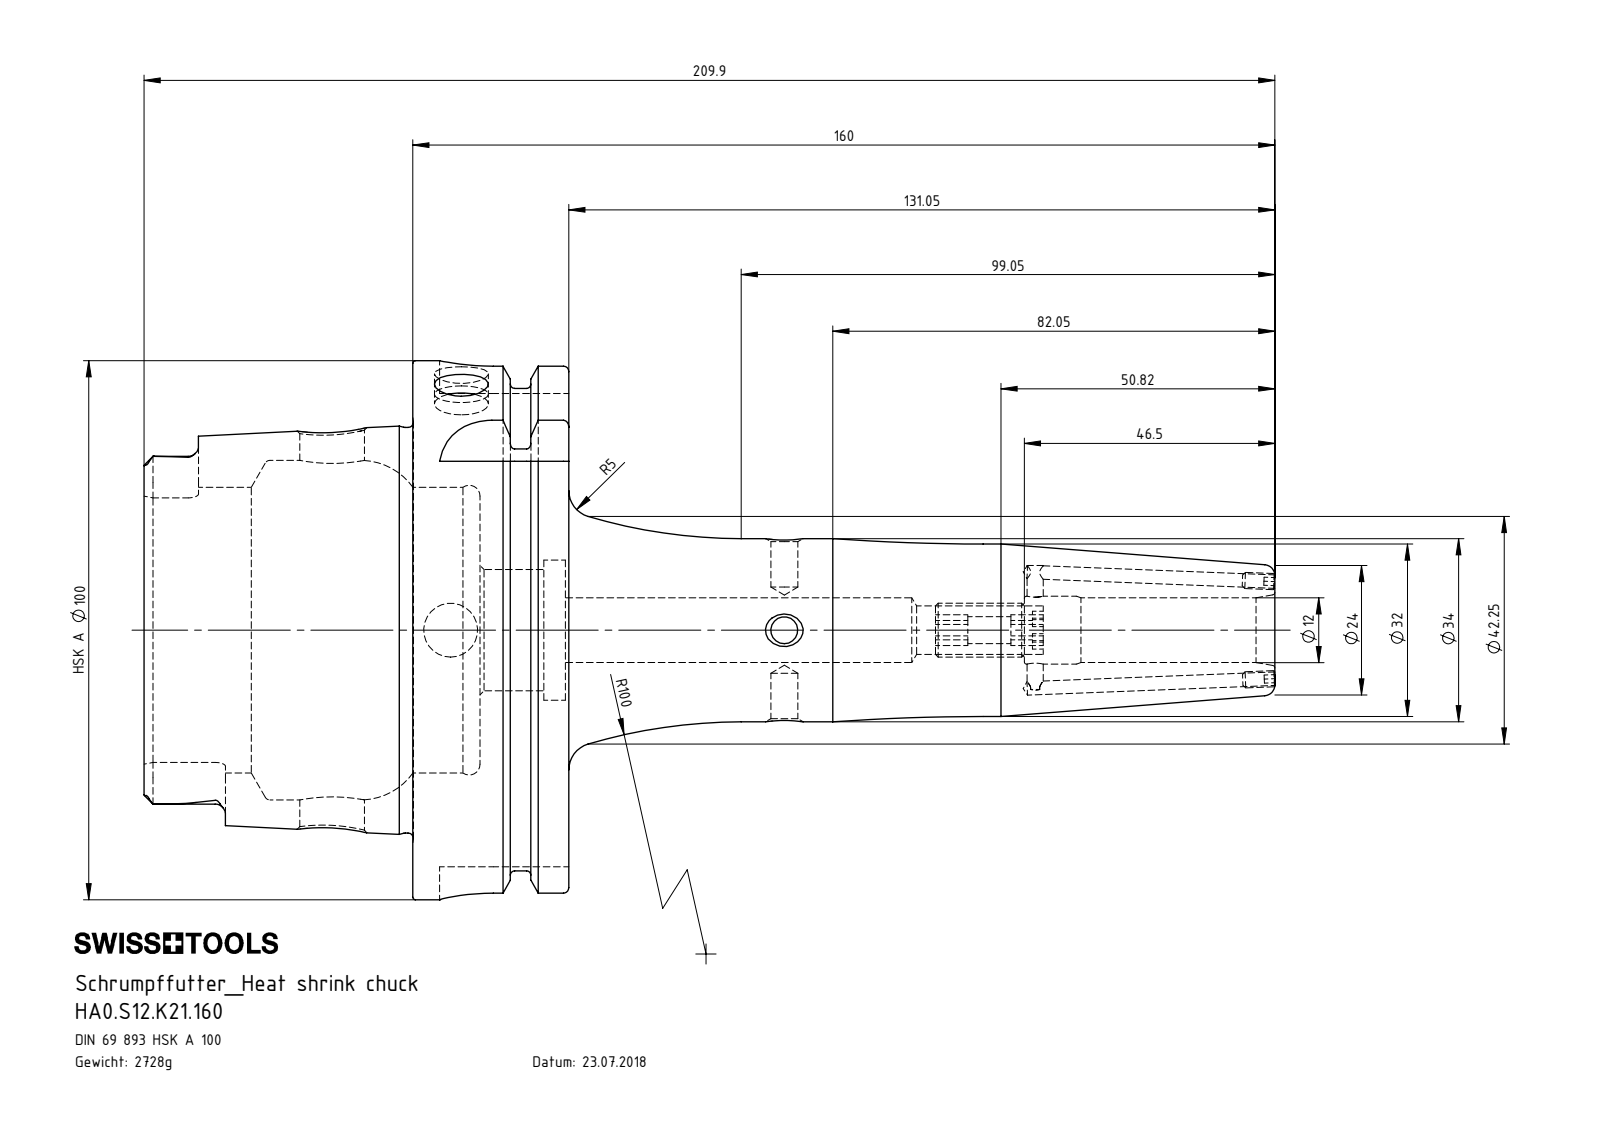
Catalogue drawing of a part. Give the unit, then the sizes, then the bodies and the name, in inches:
Units: inches
Overall size (bounding box): 8.267 × 3.937 × 3.937
Round holes (diameter × count): ⌀0.197 ×3, ⌀0.394 ×3, ⌀0.098 ×2, ⌀0.472 ×2, ⌀0.118 ×1, ⌀0.354 ×1, ⌀0.496 ×1, ⌀0.886 ×1, ⌀1.024 ×1, ⌀2.087 ×1, ⌀2.48 ×1
Round bosses / shafts (diameter × count): ⌀0.118 ×2, ⌀3.937 ×1, ⌀3.62 ×1, ⌀2.963 ×1, ⌀1.339 ×1, ⌀1.26 ×1, ⌀0.394 ×1
Partial cylindrical surfaces — rounded edges, fillets, slot ends (radius × count): R0.075 ×6, R0.192 ×4, R0.394 ×4
Main face-to-face distances: 1.14, 0.65, 0.49, 1.965, 2.455, 3.104, 3.457, 3.079, 1.114, 0.624
Hole centre spacings: 1.833, 2.439, 3.305, 5.138
Volume: 21.21 in³ · Surface area: 107.1 in²
Bodies: 4 solids, 299 faces (95 planar, 86 cylindrical, 118 other)
Part name (STEP PRODUCT): ERU-CJ2.001.006; HA0-S12.K21.160_C_Fertigbearbeitung; HA0.S12.K21.160; ERU-AN4.K01.020_A
STEP written by: SolidWorks 2017 (CONFIG_CONTROL_DESIGN)
